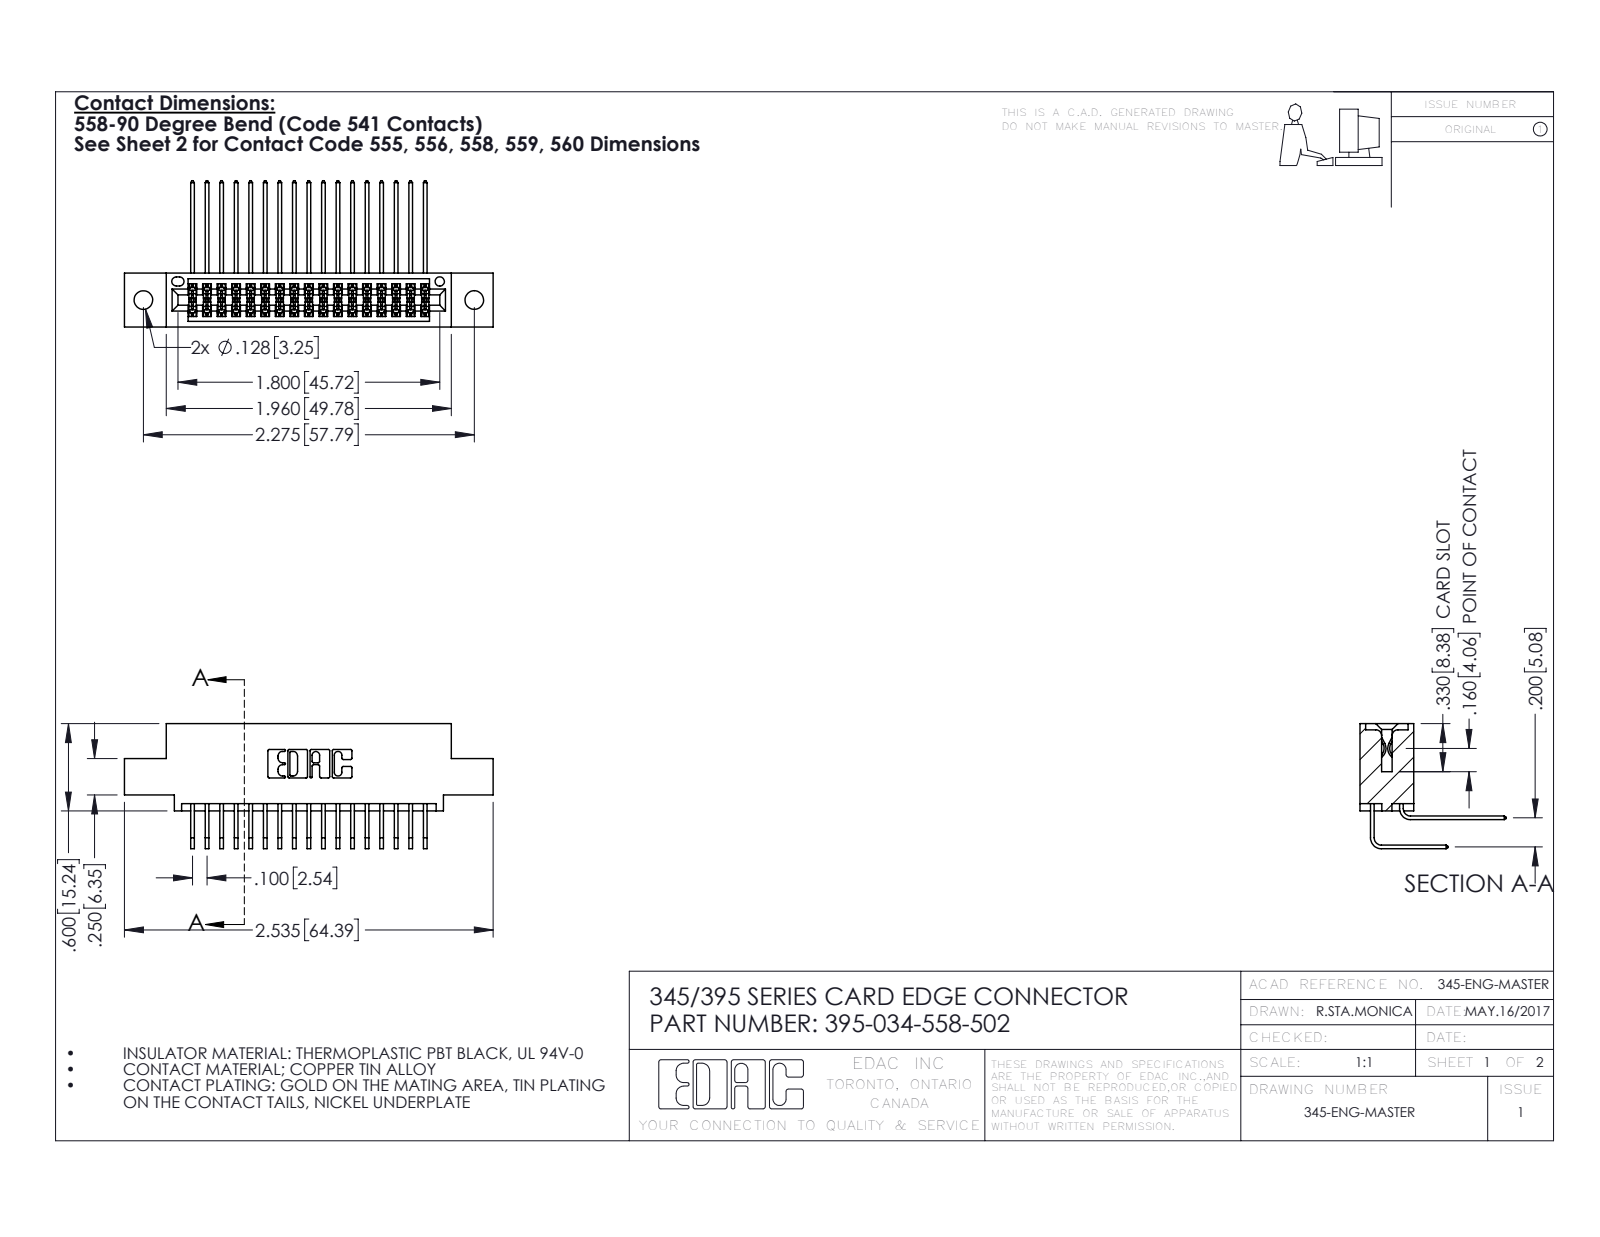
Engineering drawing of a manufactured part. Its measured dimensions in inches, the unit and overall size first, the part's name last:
Units: inches
Overall size (bounding box): 2.535 × 1.005 × 0.859
Round holes (diameter × count): ⌀0.128 ×2, ⌀0.064 ×1
Partial cylindrical surfaces — rounded edges, fillets, slot ends (radius × count): R0.006 ×52, R0.01 ×22, R0.007 ×6, R0.031 ×6, R0.026 ×3, R0.014 ×2, R0.019 ×2, R0.022 ×2
Main face-to-face distances: 0.2, 0.072, 0.298, 0.37, 0.098, 0.272, 0.025, 0.225, 0.1, 0.025
Hole centre spacings: 0.27, 2.041, 2.275
Volume: 0.373 in³ · Surface area: 14.4 in²
Bodies: 35 solids, 1898 faces (1274 planar, 624 cylindrical, 0 other)
Part name (STEP PRODUCT): 345-292-001_558 Tail - 2; 345 Part_0.110 Offset - 0.128 Dia; 345-292-001_558 559 Tail - 1; 395-034-558-502
STEP written by: SolidWorks 2016 (CONFIG_CONTROL_DESIGN)
